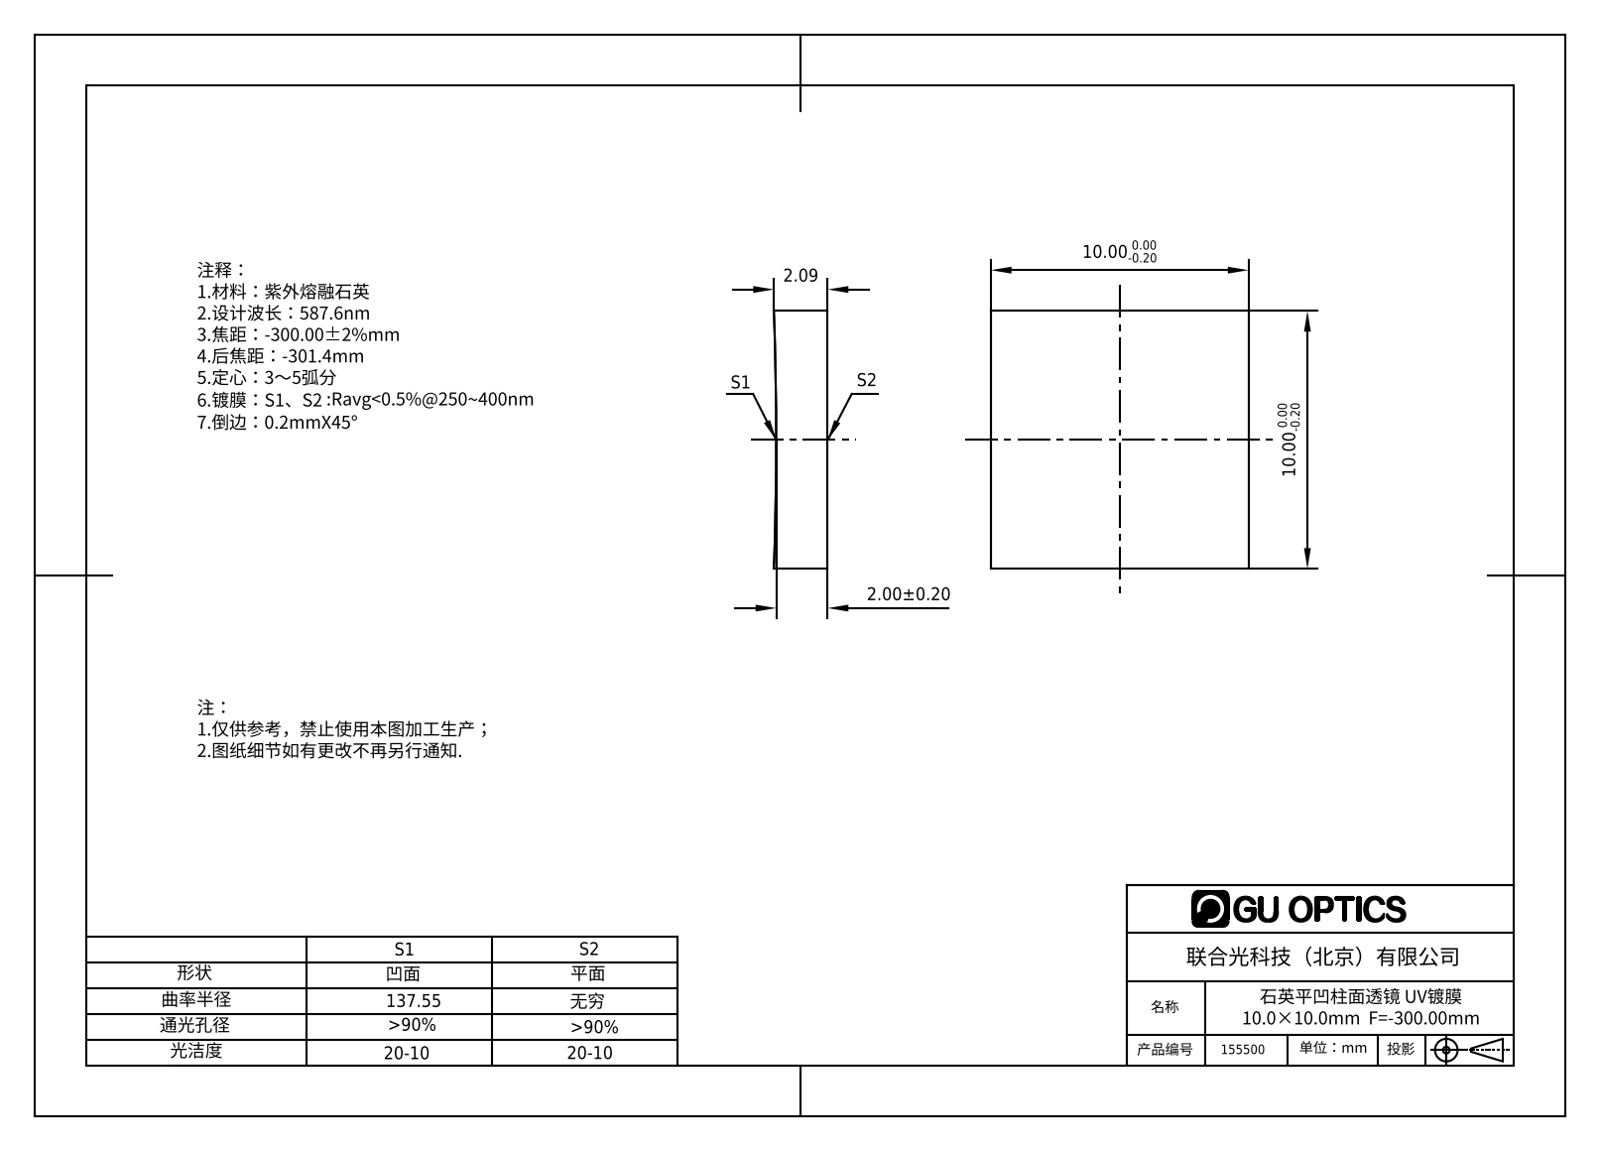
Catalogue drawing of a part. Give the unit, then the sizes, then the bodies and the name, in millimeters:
Units: millimetres
Overall size (bounding box): 10 × 10 × 2.09
Partial cylindrical surfaces — rounded edges, fillets, slot ends (radius × count): R137.55 ×1
Main face-to-face distances: 10
Volume: 203 mm³ · Surface area: 282 mm²
Bodies: 1 solid, 6 faces (5 planar, 1 cylindrical, 0 other)
Part name (STEP PRODUCT): 155474
STEP written by: SolidWorks 2016 (AUTOMOTIVE_DESIGN)
